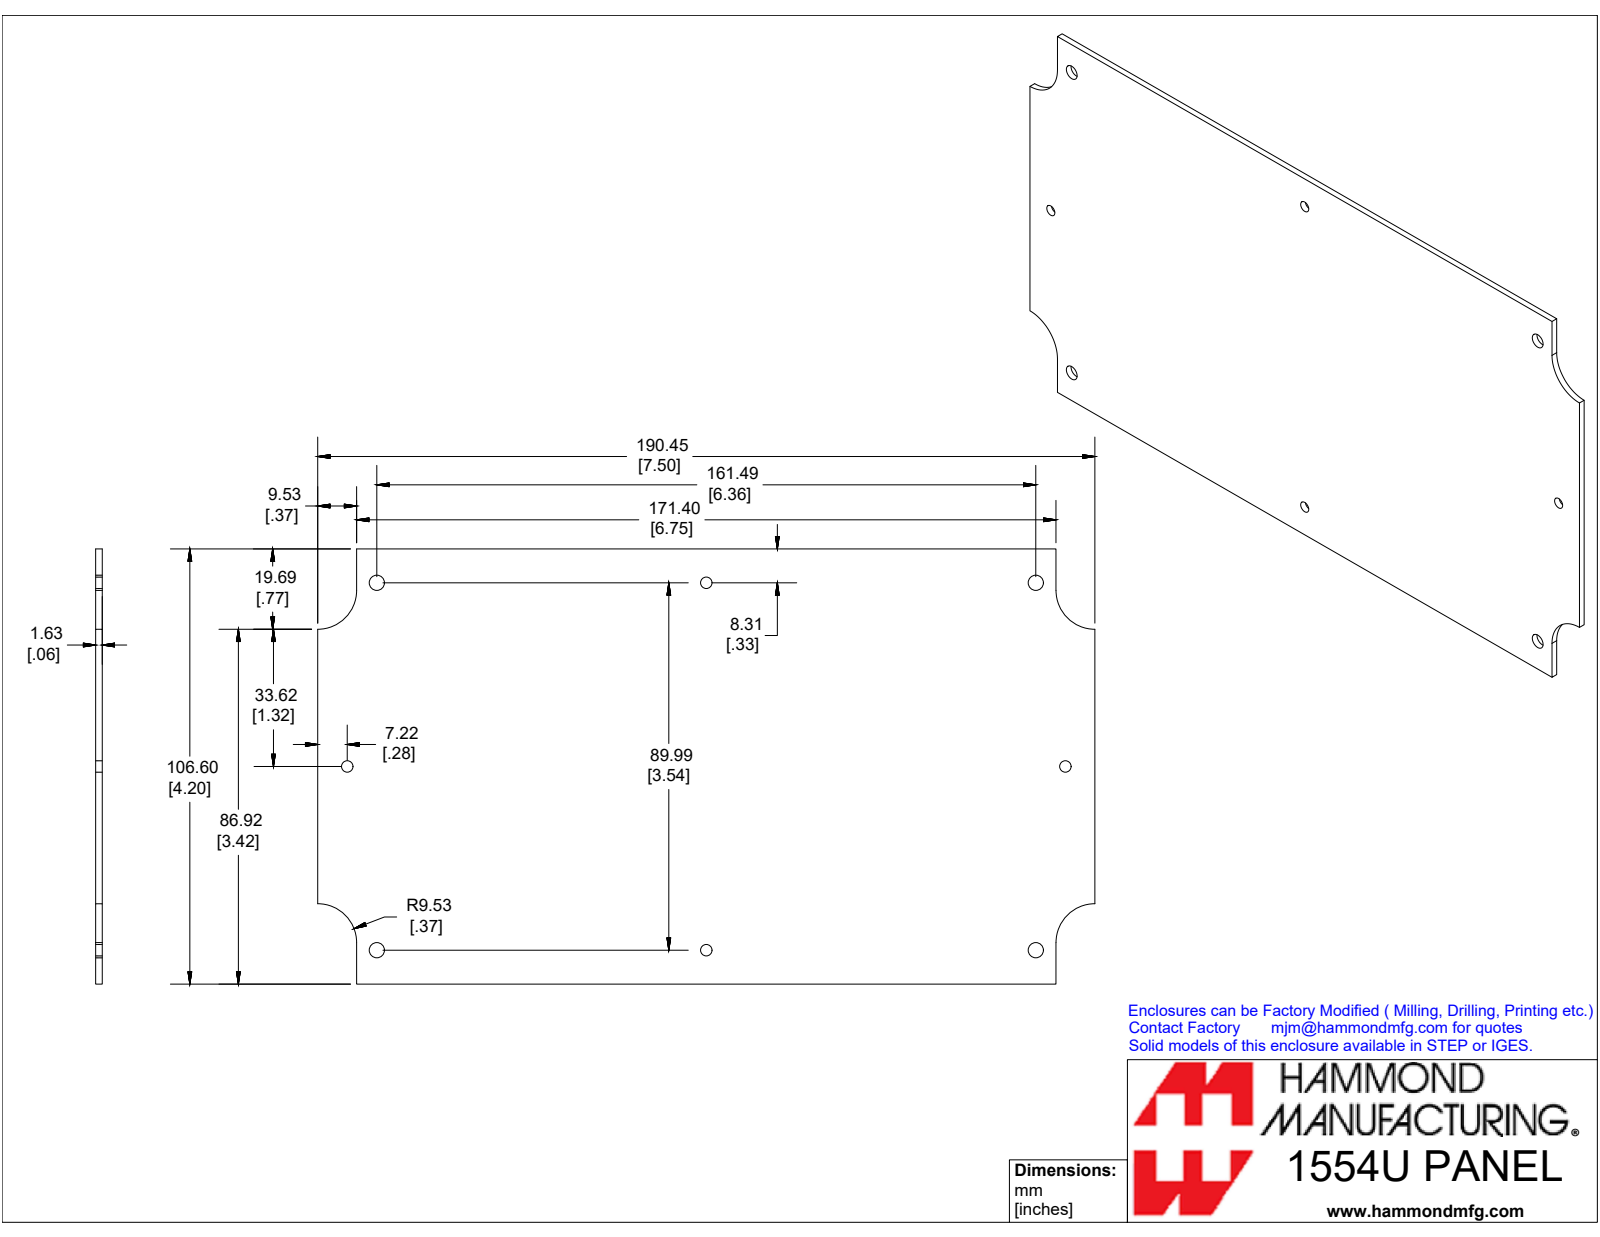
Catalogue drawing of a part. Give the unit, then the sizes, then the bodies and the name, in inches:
Units: inches
Overall size (bounding box): 7.498 × 4.197 × 0.064
Round holes (diameter × count): ⌀0.11 ×4, ⌀0.147 ×4
Partial cylindrical surfaces — rounded edges, fillets, slot ends (radius × count): R0.375 ×4
Main face-to-face distances: 0.064, 4.197, 7.498, 0.375, 7.123, 6.748
Hole centre spacings: 1.794, 3.179, 3.891, 4.761, 6.876, 3.543, 6.358, 7.279
Volume: 1.941 in³ · Surface area: 62.31 in²
Bodies: 1 solid, 22 faces (10 planar, 12 cylindrical, 0 other)
Part name (STEP PRODUCT): 1554UPL
STEP written by: SolidWorks 2019 (CONFIG_CONTROL_DESIGN)
